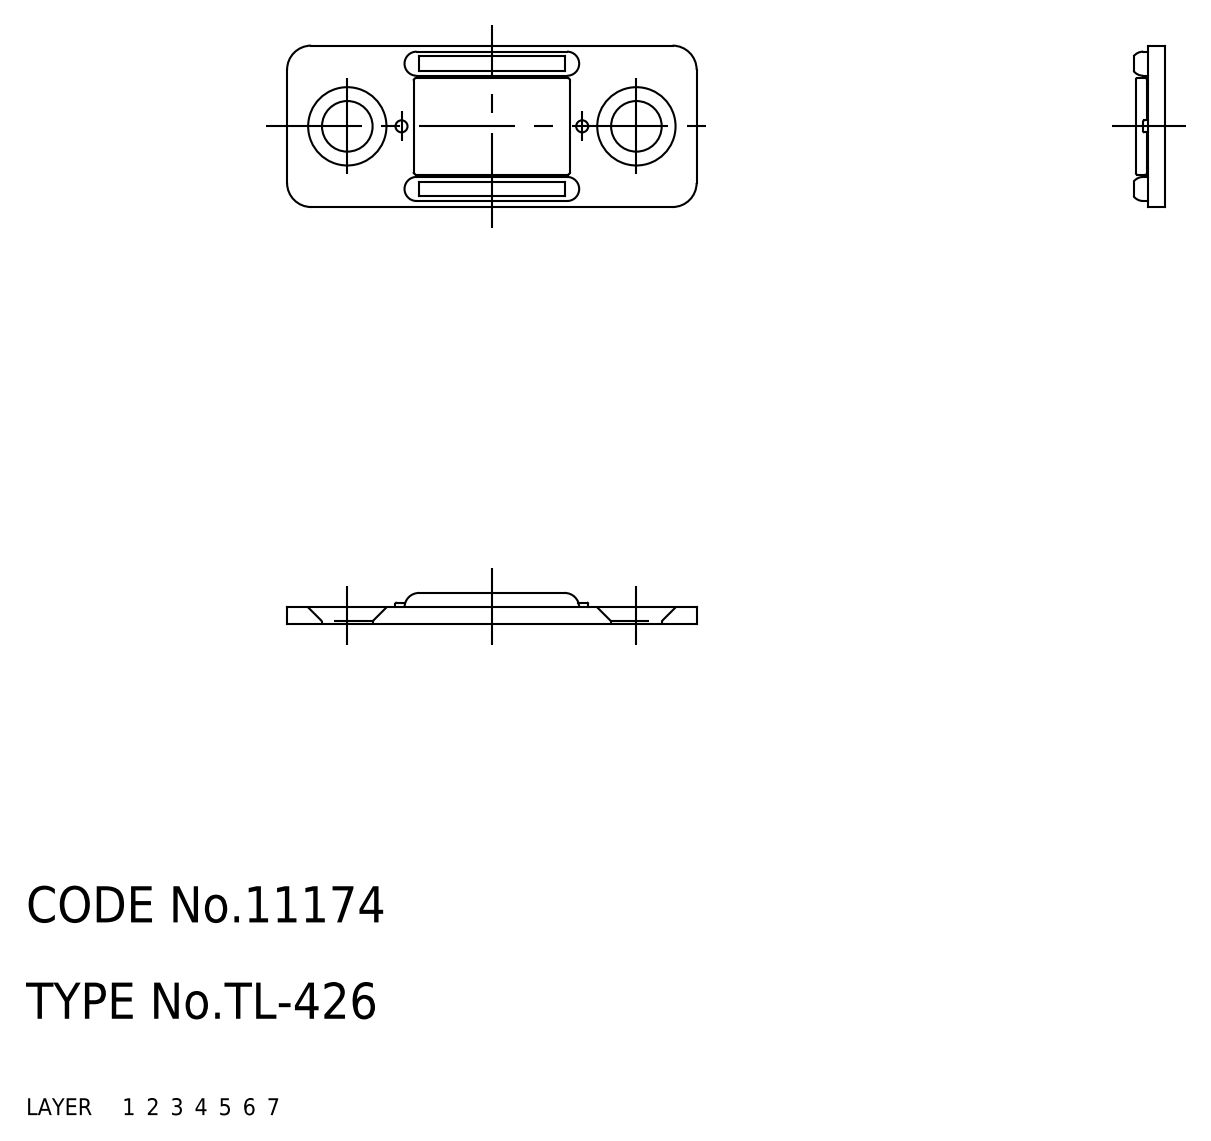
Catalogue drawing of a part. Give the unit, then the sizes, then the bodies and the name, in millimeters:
Units: millimetres
Overall size (bounding box): 34 × 13.4 × 2.6
Round holes (diameter × count): ⌀4.2 ×2
Round bosses / shafts (diameter × count): ⌀1 ×2
Partial cylindrical surfaces — rounded edges, fillets, slot ends (radius × count): R0.1 ×8, R1 ×6, R0.2 ×4, R2 ×4
Main face-to-face distances: 1.4, 1, 2.4, 13.4, 1.2, 2.6, 1.1, 0.9, 1.5, 2.7
Hole centre spacings: 24
Volume: 737 mm³ · Surface area: 1 151 mm²
Bodies: 1 solid, 76 faces (24 planar, 32 cylindrical, 20 other)
Part name (STEP PRODUCT): TL_426
STEP written by: SolidWorks 2015 (AUTOMOTIVE_DESIGN)
